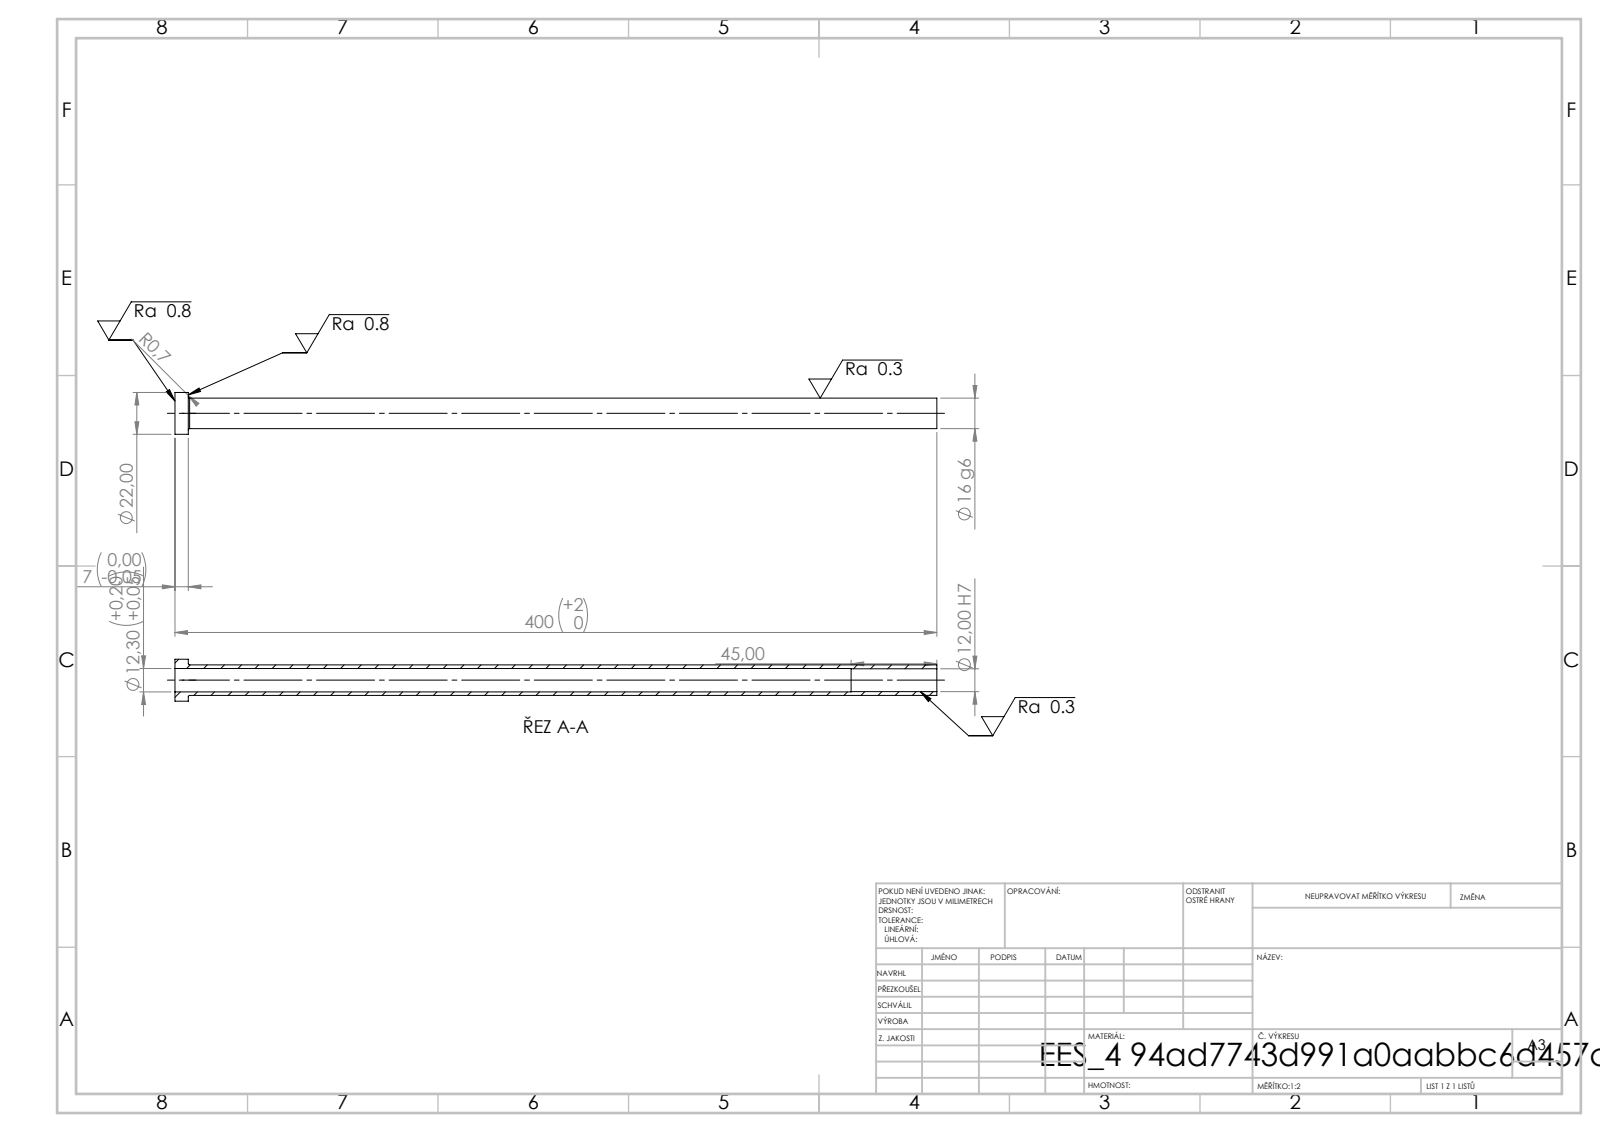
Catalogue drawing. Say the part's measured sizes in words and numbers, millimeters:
Its 3-D file was written by "SolidWorks 2019 (CONFIG_CONTROL_DESIGN)". It is 1 solid with 14 faces: 4 planar, 8 cylindrical and 2 other. Overall it measures 400 by 22 by 22 millimeters. Its volume is 34 412 cubic millimeters and its surface area 36 172 square millimeters. Round holes: 1 of diameter 12, 1 of diameter 12.3. Round bosses or shafts: 1 of diameter 22, 1 of diameter 16. The main face-to-face distances are 7, 400, 393, 355, 348, 45.
